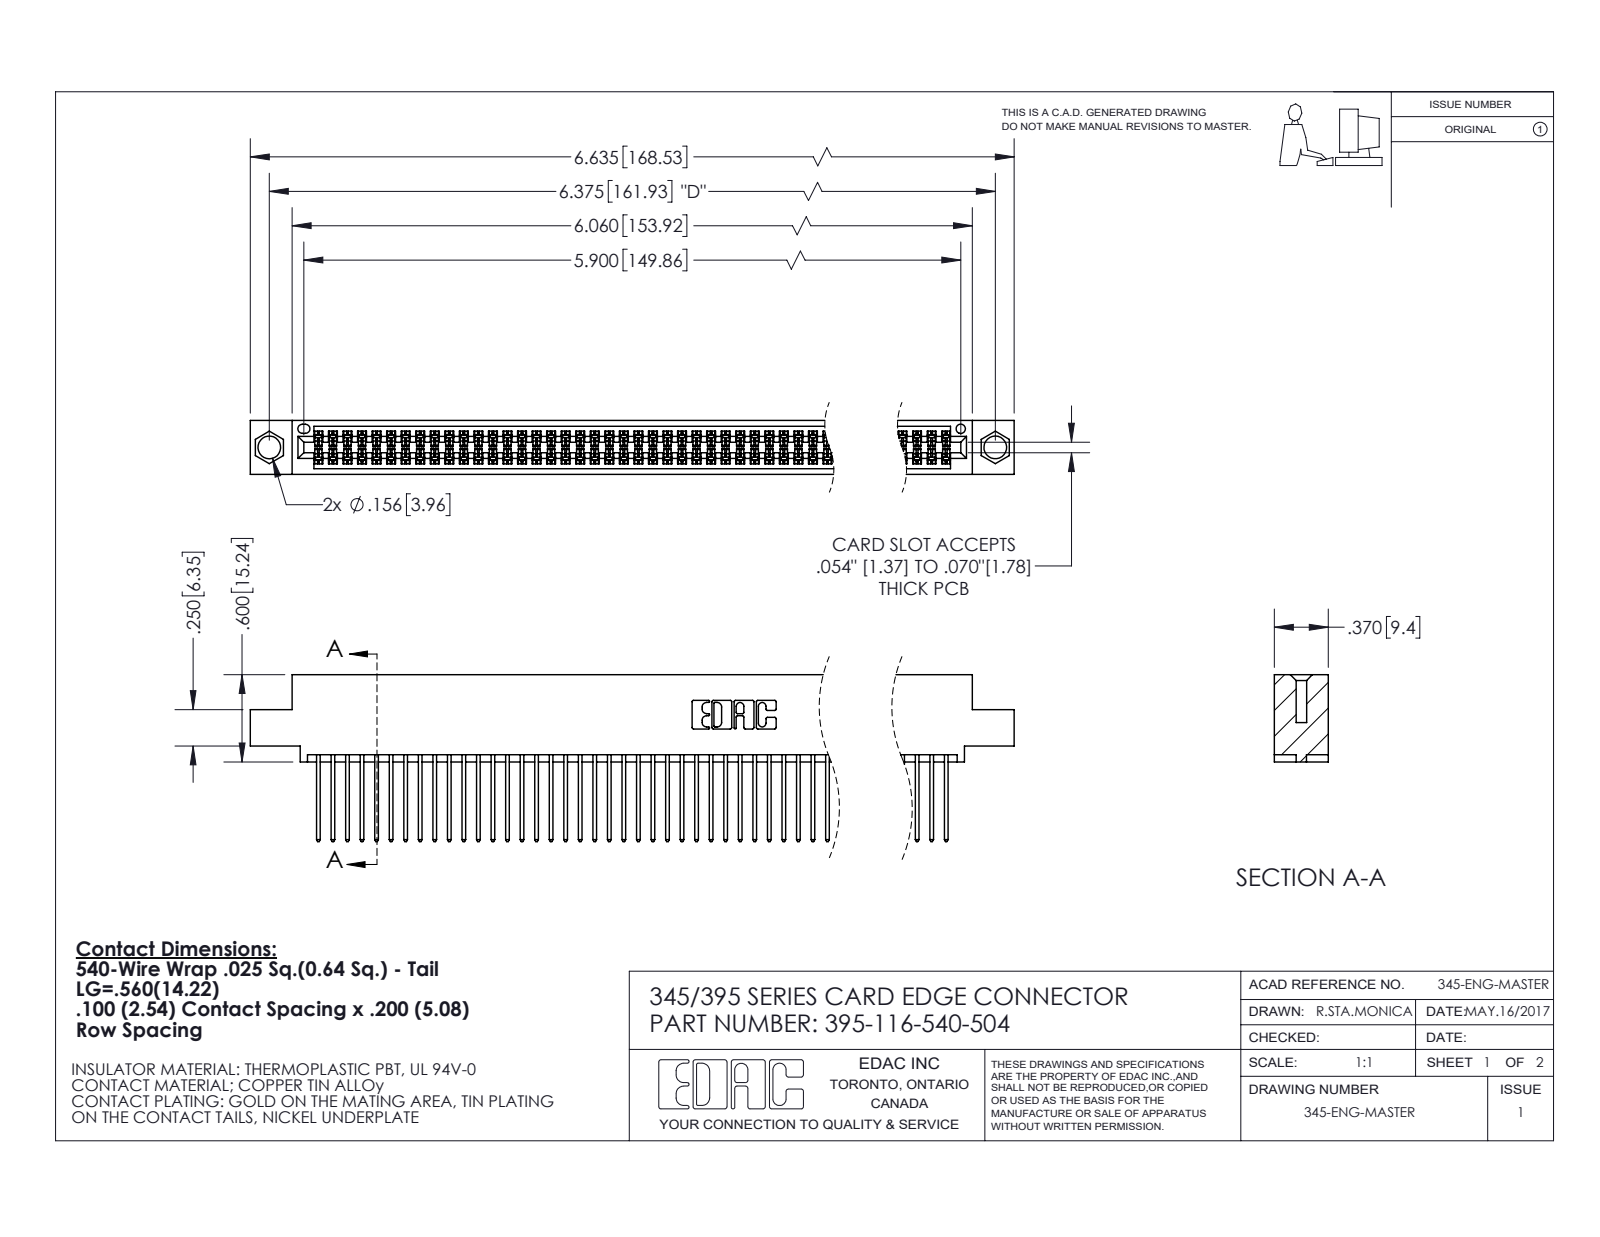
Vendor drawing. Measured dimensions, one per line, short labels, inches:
name: 395-116-540-504; 345 Part_0.110 Offset - 0.156 Dia-TI; 345-292-001_345-293-140
written by: SolidWorks 2020 (CONFIG_CONTROL_DESIGN)
unit: in
bodies: 117 solids, 5944 faces (3926 planar, 2018 cylindrical, 0 other)
size: 6.635 × 1.147 × 0.37
volume: 1.024 in³; area: 42 in²
holes: 2× ⌀0.156, 1× ⌀0.064
rounds: 174× R0.006, 116× R0.01, 22× R0.01, 6× R0.007, 6× R0.031, 3× R0.026, 2× R0.014, 2× R0.019
face distances: 0.298, 0.072, 0.2, 0.098, 0.272, 0.025, 0.37, 0.225, 0.175, 0.149
hole spacings: 0.27, 6.139, 6.375
